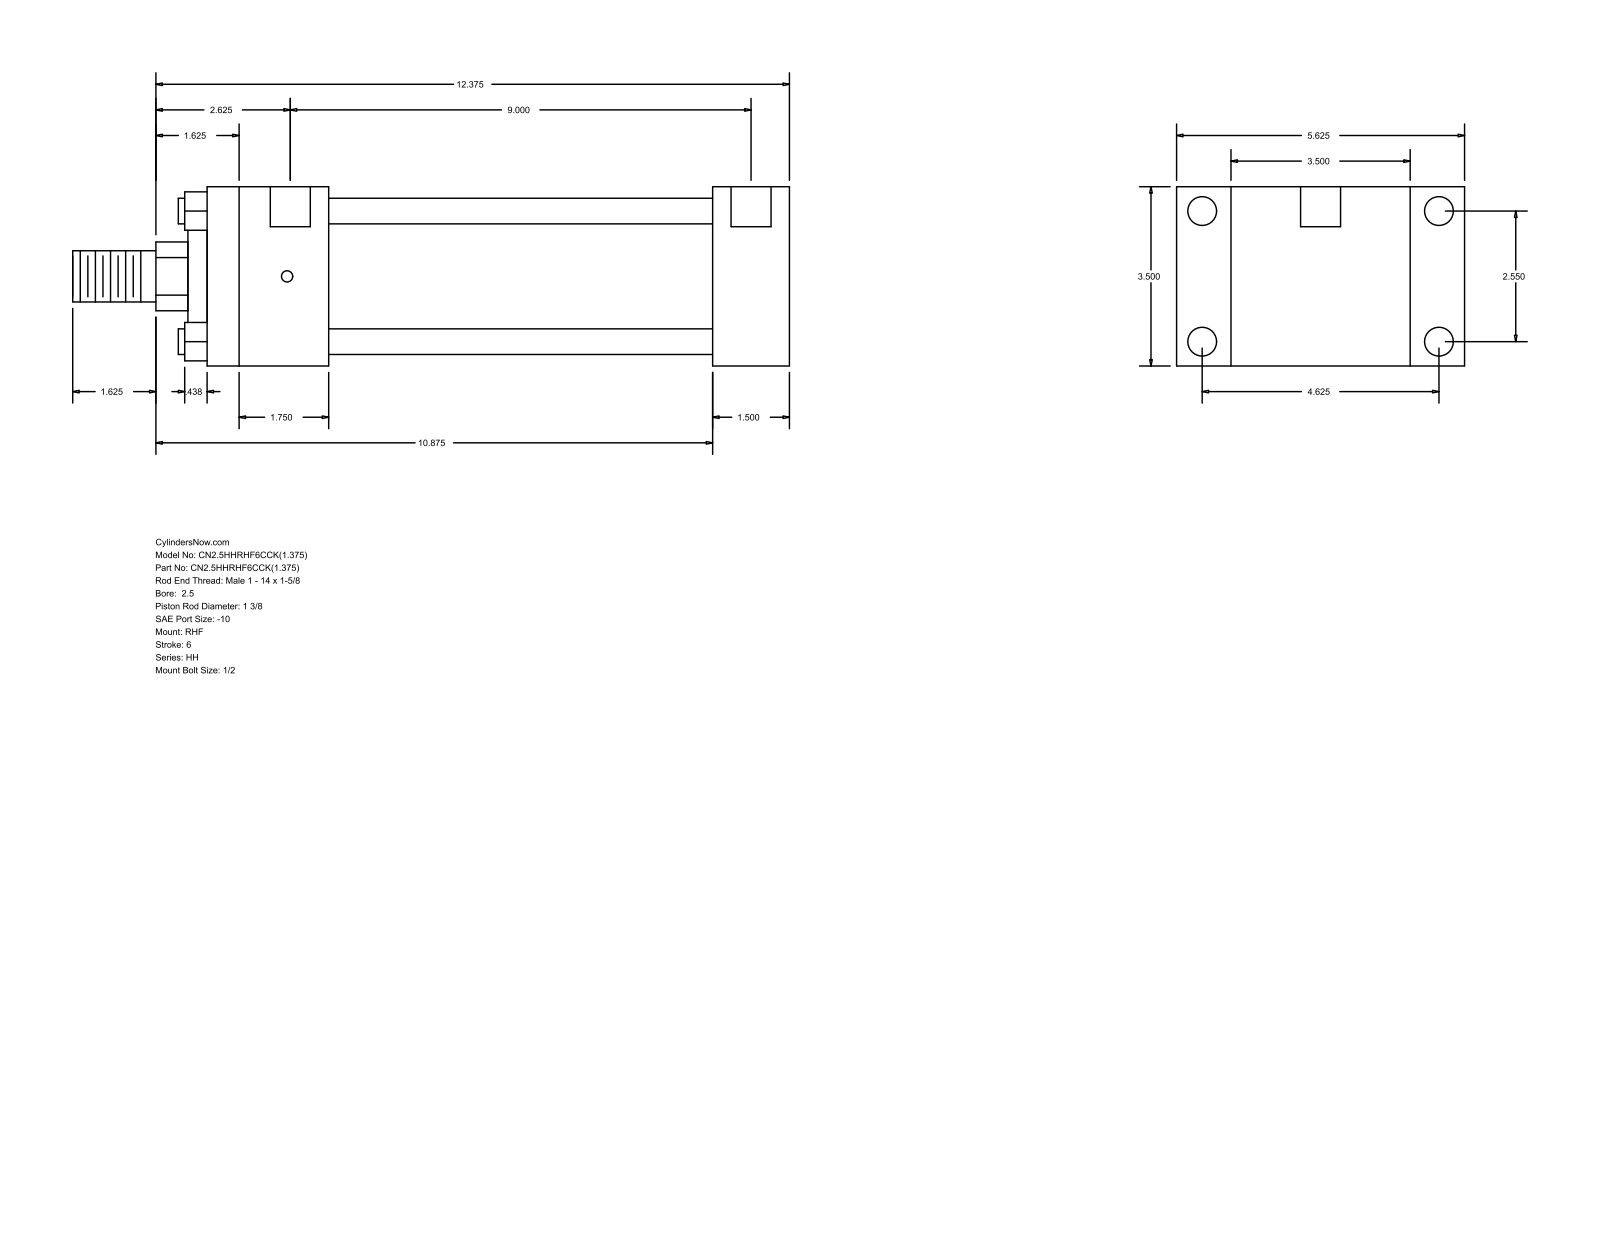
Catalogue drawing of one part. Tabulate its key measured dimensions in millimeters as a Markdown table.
| quantity | value |
| --- | --- |
| part name | HH_RHF__0250_1.375 |
| STEP written by | GSSL Pune (CONFIG_CONTROL_DESIGN) |
| units | millimeters |
| bodies | 0 solids, 88 faces (60 planar, 28 cylindrical, 0 other) |
| overall size | 355.6 × 142.88 × 88.9 |
| round holes (diameter × count) | 5.56 × 4, 14.3 × 4, 19.84 × 2 |
| round bosses / shafts (diameter × count) | 12.7 × 4, 73.03 × 1, 50.8 × 1, 34.92 × 1, 25.4 × 1 |
| partial cylindrical surfaces (radius × count) | 17.06 × 1 |
| main face-to-face distances | 88.9, 38.09, 26.99, 115.89, 250.83, 288.92, 142.88, 60.32, 190.51, 228.6 |
| hole center spacings | 64.76, 117.48, 134.15, 231.77, 1.58, 1.59, 228.6, 230.18 |
